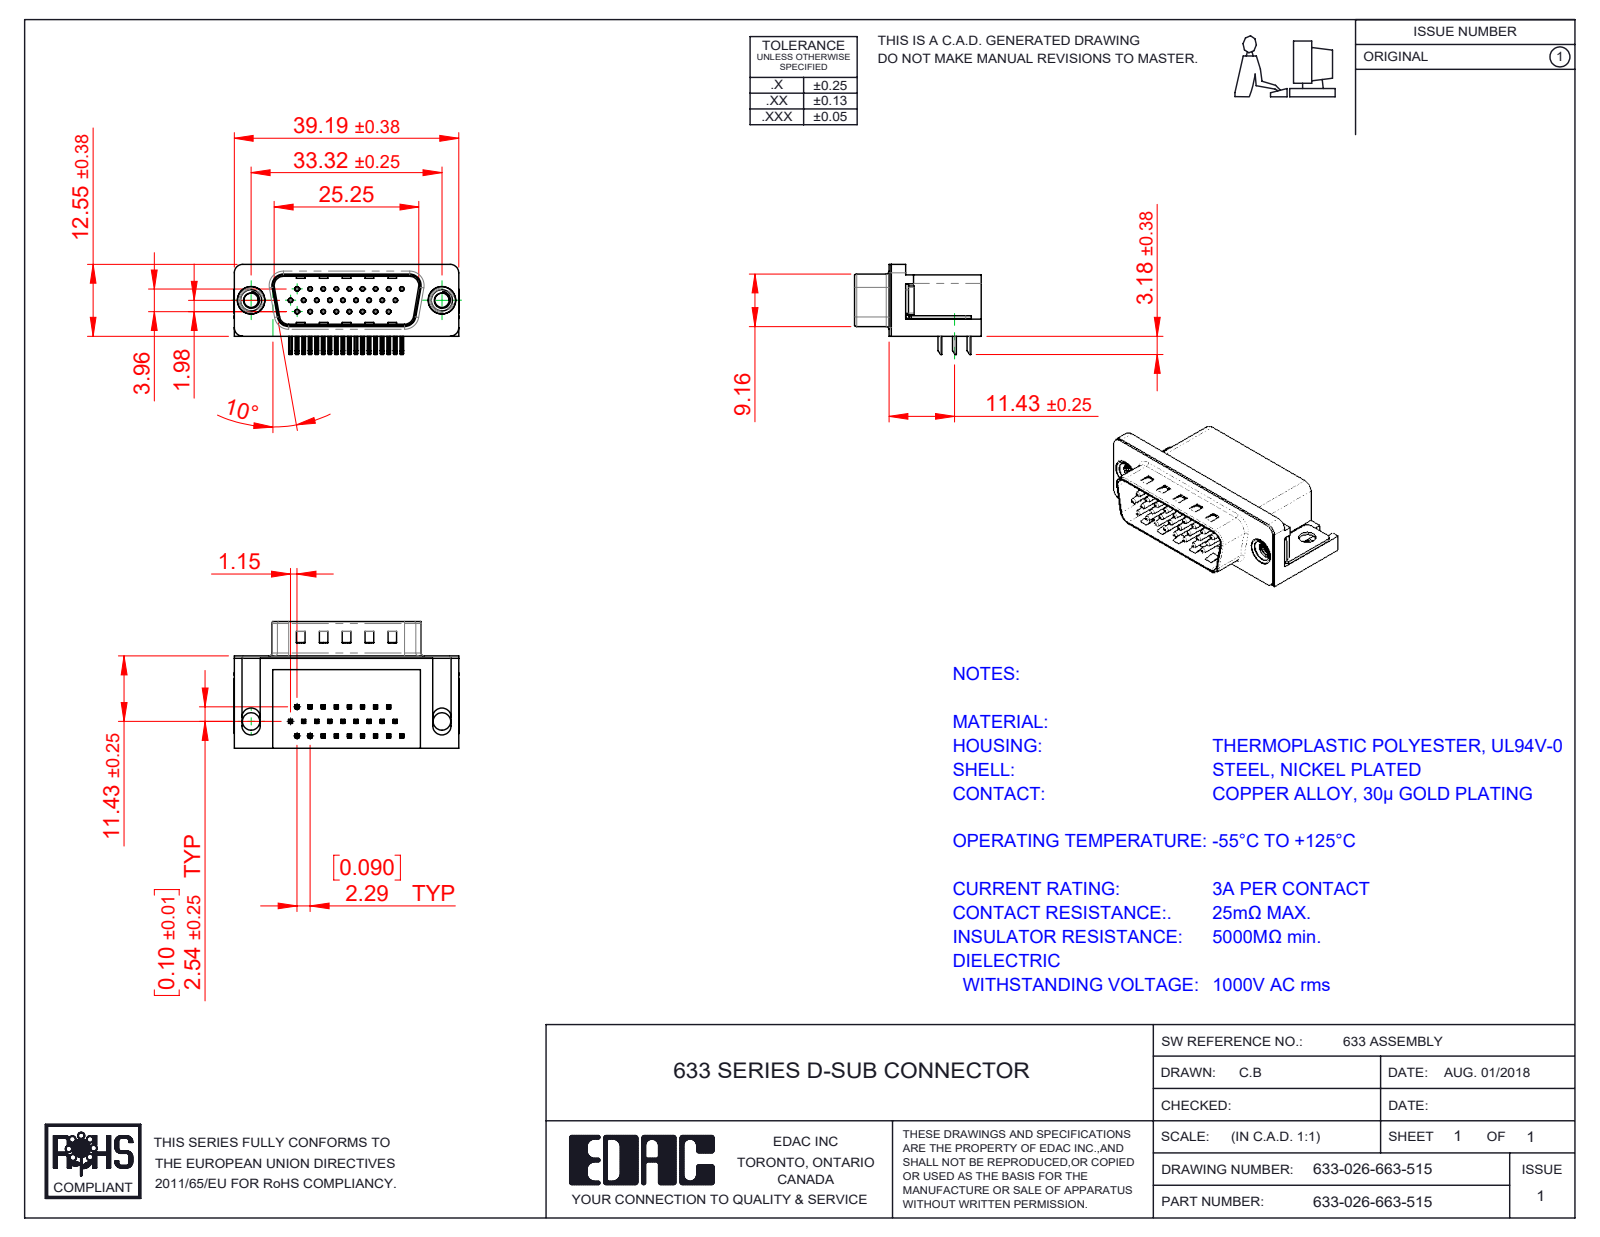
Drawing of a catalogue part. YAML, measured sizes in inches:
part_name: "633 Thru Hole Board Mount; 633 Contact Middle; 633 Shell_26 Contact; 633 Contact Bottom (+4 more)"
step_written_by: "SolidWorks 2016 (CONFIG_CONTROL_DESIGN)"
units: inches
bodies: {solids: 32, faces: 2302, planar: 1419, cylindrical: 682, other: 201}
overall_size: [1.544, 0.87, 0.619]
volume: 0.341
surface_area: 11.22
round_holes:
  - {diameter: 0.014, count: 26}
  - {diameter: 0.031, count: 26}
  - {diameter: 0.098, count: 2}
  - {diameter: 0.12, count: 2}
  - {diameter: 0.157, count: 2}
  - {diameter: 0.189, count: 2}
  - {diameter: 0.197, count: 2}
round_bosses_or_shafts:
  - {diameter: 0.03, count: 26}
  - {diameter: 0.193, count: 2}
  - {diameter: 0.187, count: 2}
  - {diameter: 0.154, count: 2}
partial_cylinders:
  - {radius: 0.01, count: 112}
  - {radius: 0.005, count: 52}
  - {radius: 0.039, count: 16}
  - {radius: 0.02, count: 9}
  - {radius: 0.059, count: 8}
  - {radius: 0.063, count: 8}
  - {radius: 0.035, count: 4}
  - {radius: 0.079, count: 4}
face_to_face_distances: [0.016, 0.407, 0.618, 0.114, 0.098, 0.634, 0.02, 0.345, 0.014, 0.421]
hole_center_spacings: [0.09, 0.18, 0.09, 0.156, 0.238, 0.18, 0.27, 0.312]
